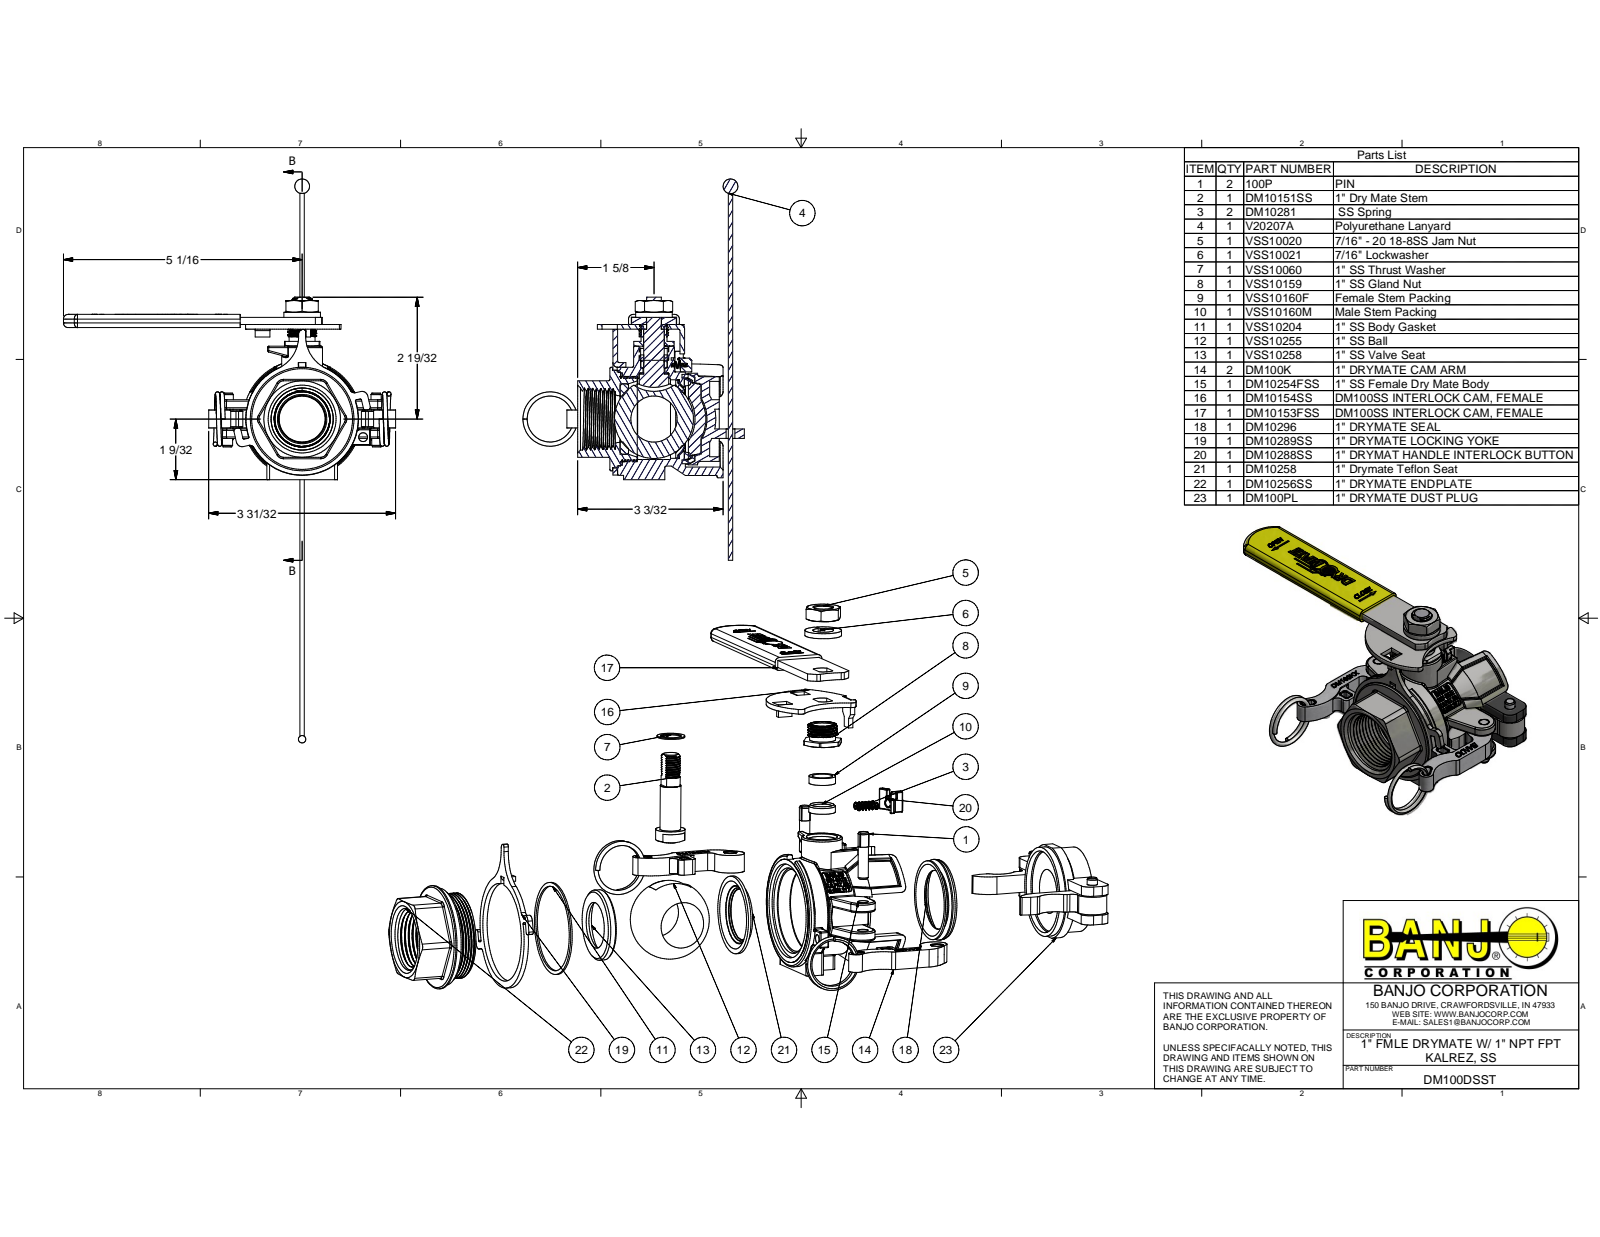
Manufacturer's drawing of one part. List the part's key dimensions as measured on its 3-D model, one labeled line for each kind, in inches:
Part name (STEP PRODUCT): 100P; DM10151SS; DM10281; V20207A (+8 more)
STEP written by: Autodesk Inventor 2015 (AUTOMOTIVE_DESIGN)
Units: inches
Bodies: 38 solids, 2858 faces (1312 planar, 592 cylindrical, 954 other)
Overall size (bounding box): 11.984 × 7.048 × 4.935
Volume: 12.23 in³ · Surface area: 201.7 in²
Round holes (diameter × count): ⌀0.125 ×3, ⌀0.218 ×2, ⌀0.219 ×2, ⌀0.225 ×2, ⌀0.228 ×2, ⌀0.245 ×2, ⌀0.187 ×1, ⌀0.188 ×1, ⌀0.383 ×1, ⌀0.432 ×1, ⌀0.434 ×1, ⌀0.438 ×1
Round bosses / shafts (diameter × count): ⌀0.227 ×4, ⌀0.217 ×4, ⌀0.22 ×3, ⌀0.01 ×2, ⌀2.39 ×1, ⌀2.2 ×1, ⌀2.07 ×1, ⌀2 ×1
Partial cylindrical surfaces — rounded edges, fillets, slot ends (radius × count): R0.03 ×69, R0.016 ×50, R0.02 ×27, R0.1 ×21, R0.125 ×14, R0.04 ×8, R0.06 ×8, R0.09 ×8
Main face-to-face distances: 0.065, 0.155, 0.215, 0.06, 0.15, 0.22, 0.6, 0.22, 0.2, 0.02
Hole centre spacings: 0.621, 1.076, 0.796, 1.609, 1.662, 1.902, 2.078, 3.253
